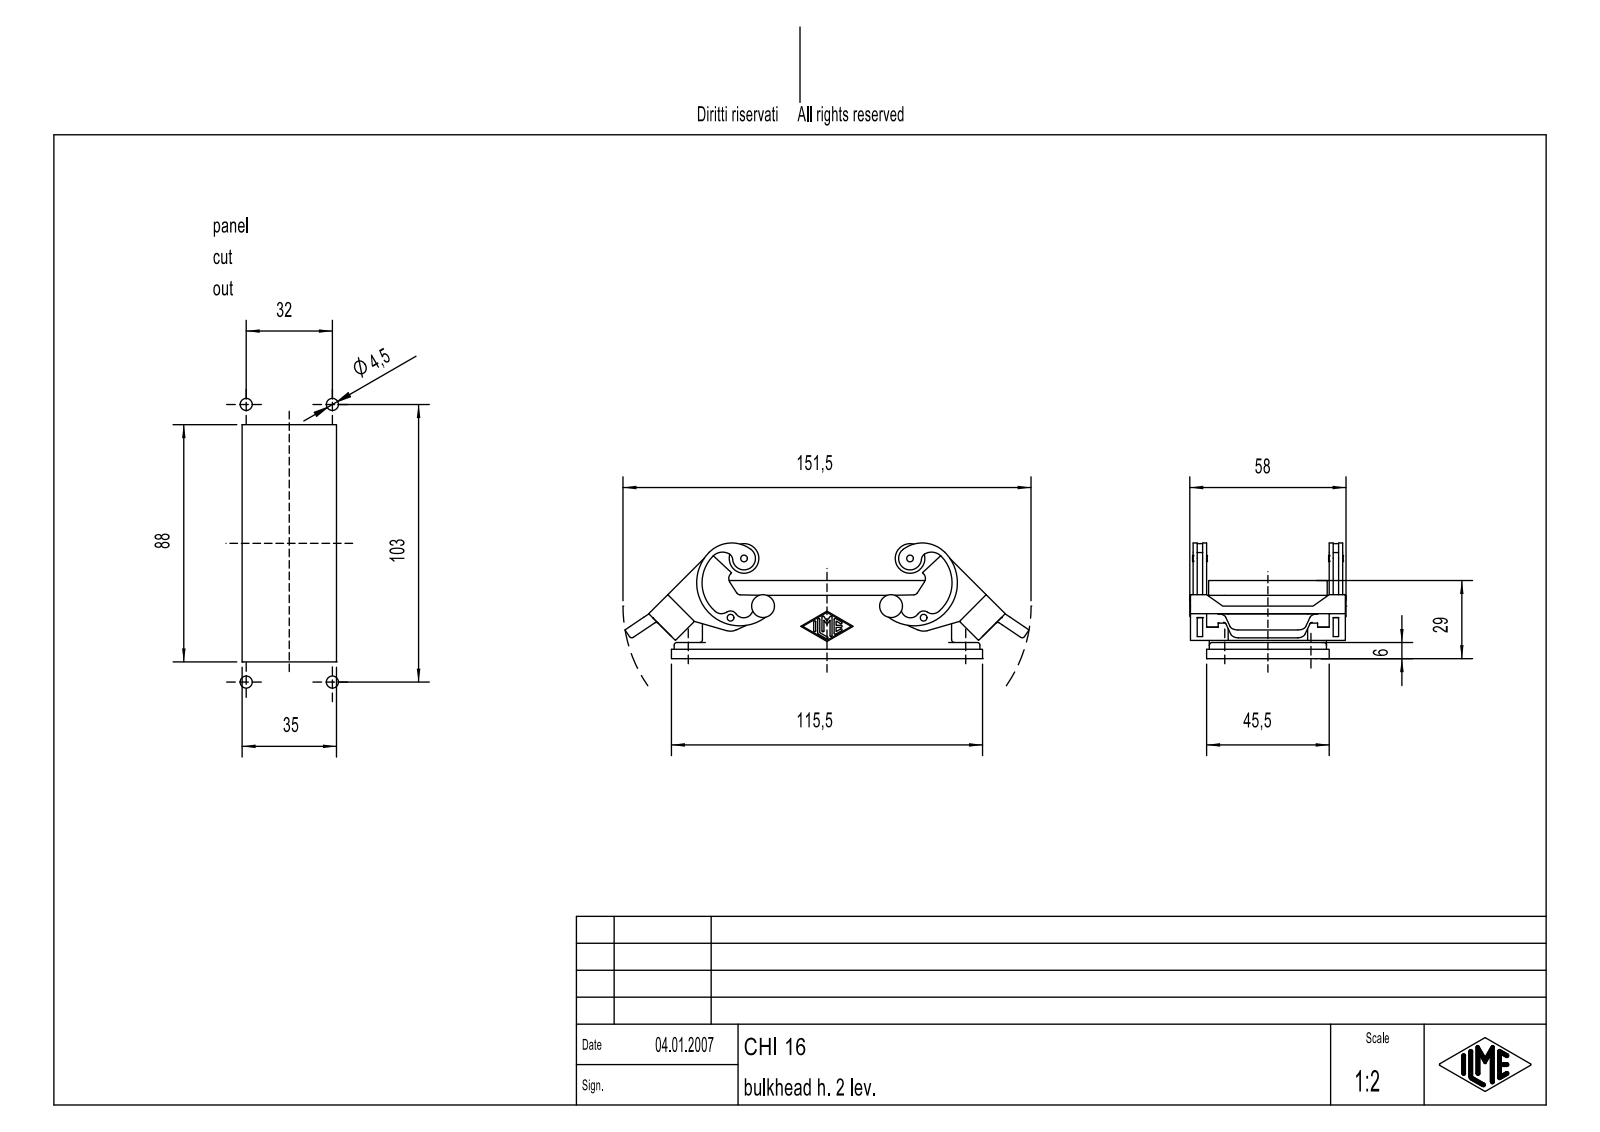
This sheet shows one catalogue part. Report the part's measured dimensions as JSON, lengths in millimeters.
{"part_name": "CHI 16", "step_written_by": "Autodesk Inventor 7 (AUTOMOTIVE_DESIGN)", "units": "millimeters", "bodies": {"solids": 1, "faces": 749, "planar": 201, "cylindrical": 220, "other": 328}, "overall_size": [149.99, 58, 42.94], "volume_mm3": 53083, "surface_area_mm2": 36692, "round_holes": [[2, 4], [4.5, 4], [4.6, 4], [2.5, 2]], "round_bosses_or_shafts": [[11, 2], [5, 2], [3, 2]], "partial_cylinders_radius": [[0.38, 14], [1, 14], [3, 12], [2.5, 10], [3.5, 8], [5, 8], [6, 8], [4, 6]], "face_to_face_distances": [3, 4, 40.5, 1, 0.75, 3.5, 2.5, 40.75, 50.5, 4.25], "hole_center_spacings": [22.56, 32, 70.19, 103, 107.86, 61.64, 71.68]}
